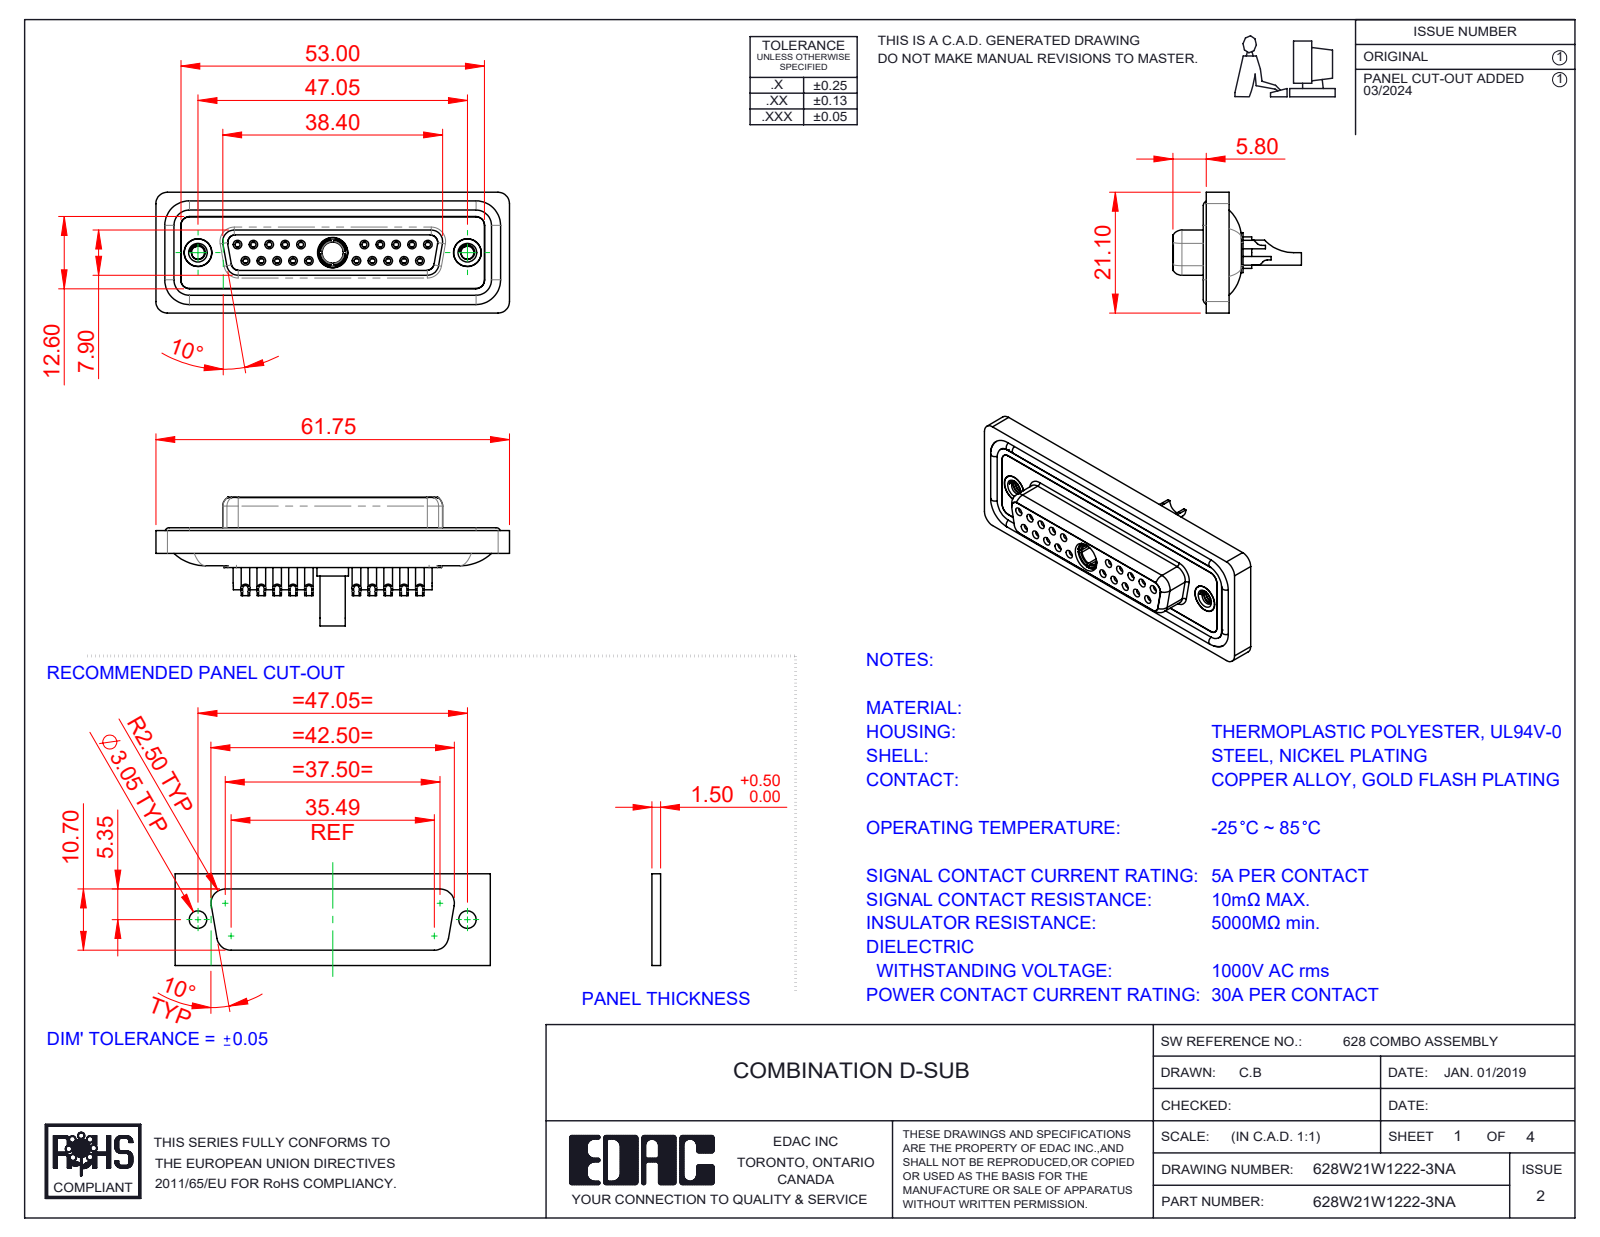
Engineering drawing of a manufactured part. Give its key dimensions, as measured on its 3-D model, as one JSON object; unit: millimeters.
{"part_name": "628Combo Housing_21W1; 628Combo Shell Rear_25 Contacts; 628Combo Waterproof Housing_25 Contacts; 628W21W1222-3NA (+5 more)", "step_written_by": "SolidWorks 2023 (CONFIG_CONTROL_DESIGN)", "units": "millimeters", "bodies": {"solids": 29, "faces": 1564, "planar": 477, "cylindrical": 636, "other": 451}, "overall_size": [61.75, 22.45, 21.1], "volume_mm3": 8440, "surface_area_mm2": 14317, "round_holes": [[0.9, 20], [1, 20], [1.1, 20], [1.5, 20], [2, 20], [1.6, 10], [1.7, 10], [4.85, 3], [2.26, 2], [4, 2], [4.05, 2], [5, 2]], "round_bosses_or_shafts": [[2.2, 20], [1.6, 14], [4.95, 2], [4.8, 2], [5.5, 1], [5.2, 1], [4.96, 1], [4.75, 1]], "partial_cylinders_radius": [[1.5, 22], [2, 18], [1.35, 8], [1.6, 8], [1, 6], [0.25, 4], [0.5, 4], [0.6, 4]], "face_to_face_distances": [0.4, 1.8, 7.45, 5.65, 6.6, 0.5, 1.6, 7.05, 2.9, 1.1], "hole_center_spacings": [3.16, 2.77, 5.54, 5.03, 8.31, 7.48, 16.62, 19.39]}
